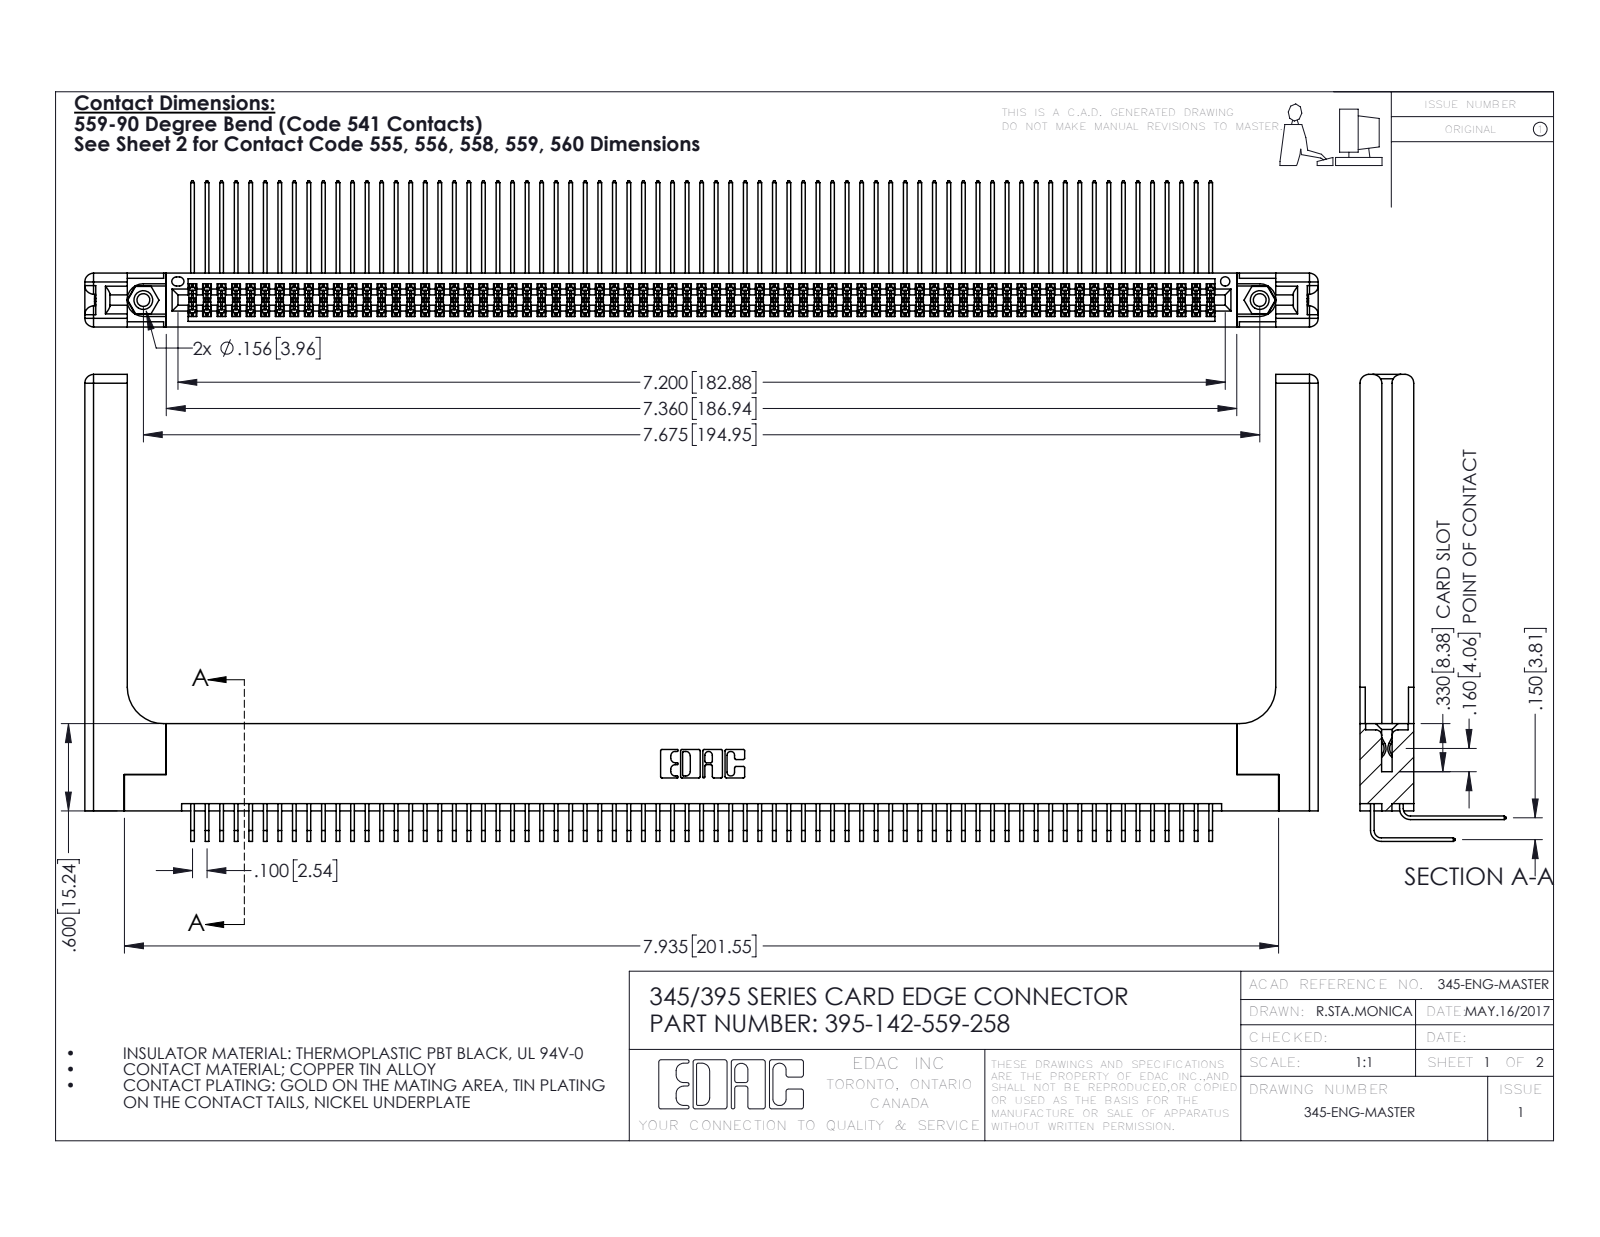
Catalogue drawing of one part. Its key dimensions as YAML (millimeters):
part_name: "395-142-559-258; 345-292-001_559 Tail - 2; 345 Part_Flush Mounting Lugs - 0.156 Dia-TH; 345-220-058_345-220-058 (+2 more)"
step_written_by: "SolidWorks 2016 (CONFIG_CONTROL_DESIGN)"
units: millimeters
bodies: {solids: 147, faces: 7766, planar: 5198, cylindrical: 2508, other: 60}
overall_size: [215.4, 81.5, 25.5]
volume: 30480
surface_area: 42010
round_holes:
  - {diameter: 2.3, count: 2}
  - {diameter: 3.2, count: 2}
  - {diameter: 4, count: 2}
  - {diameter: 1.6, count: 1}
round_bosses_or_shafts:
  - {diameter: 3.9, count: 2}
partial_cylinders:
  - {radius: 0.2, count: 284}
  - {radius: 0.3, count: 22}
  - {radius: 1.5, count: 16}
  - {radius: 0.2, count: 6}
  - {radius: 0.8, count: 6}
  - {radius: 0.7, count: 3}
  - {radius: 0.4, count: 2}
  - {radius: 0.5, count: 2}
face_to_face_distances: [1.8, 7.6, 9.4, 5.1, 2.5, 6.9, 0.6, 5.7, 4.4, 3.8]
hole_center_spacings: [6.9, 189, 194.9]
